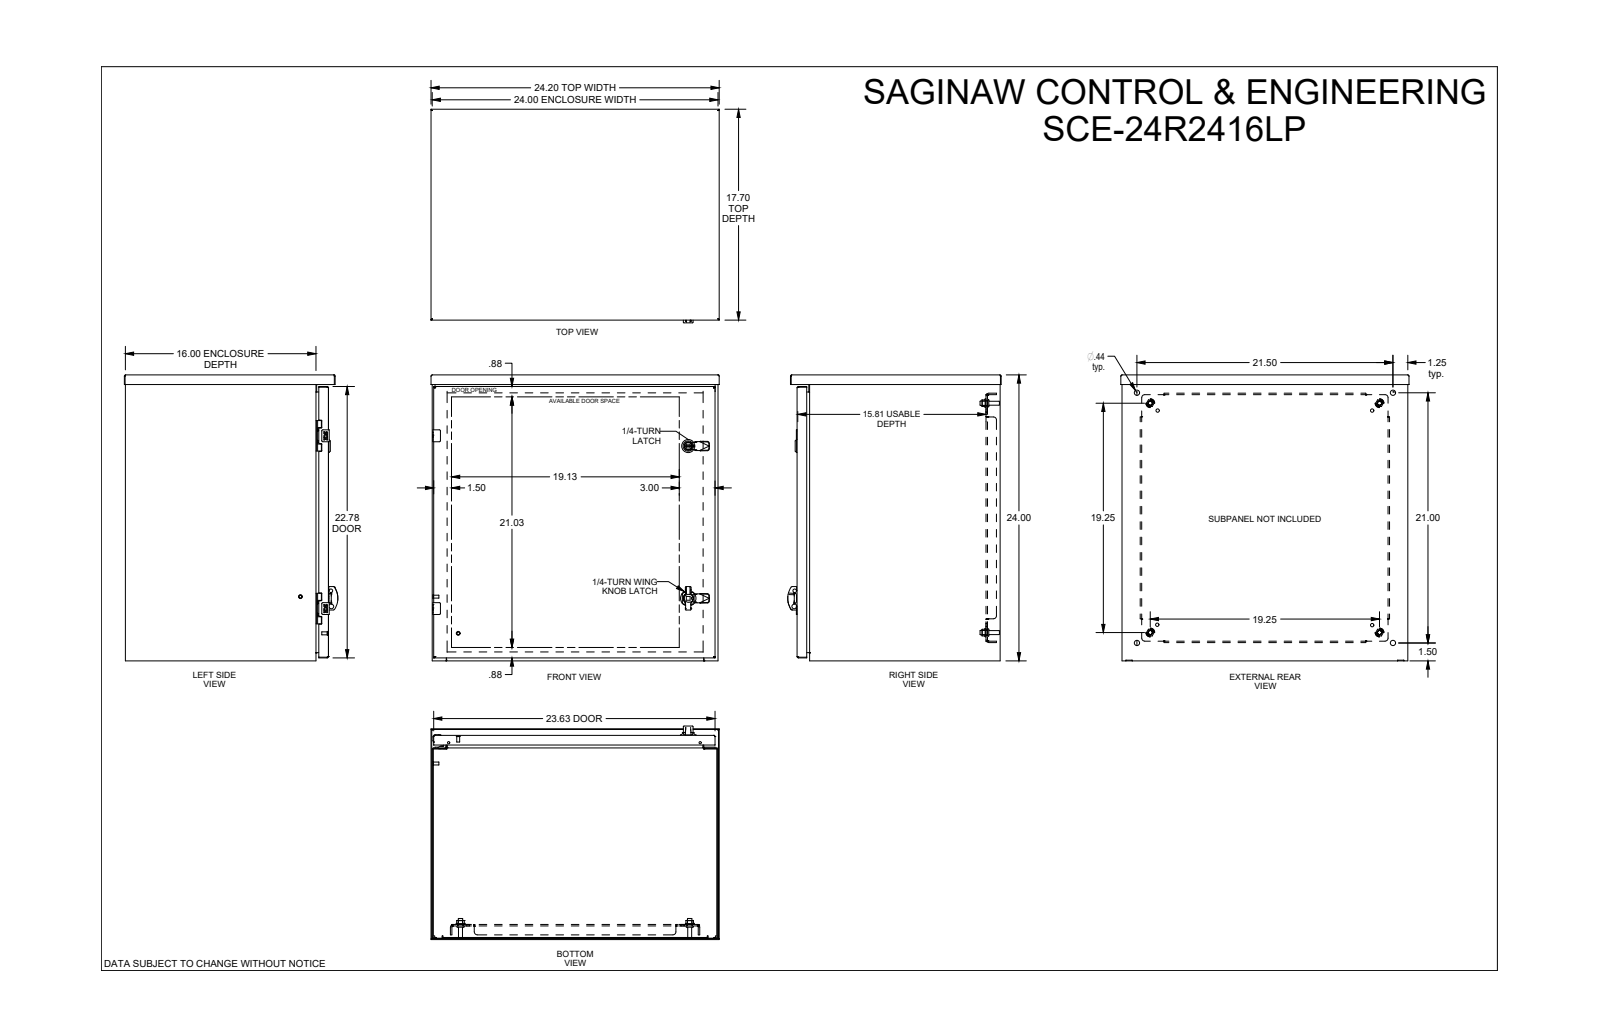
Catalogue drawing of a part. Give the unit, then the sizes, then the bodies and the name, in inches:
Units: inches
Overall size (bounding box): 24.2 × 24 × 17.927
Round holes (diameter × count): ⌀0.172 ×4, ⌀0.205 ×4, ⌀0.244 ×4, ⌀0.266 ×4, ⌀0.281 ×4, ⌀0.367 ×4, ⌀0.375 ×4, ⌀0.438 ×4, ⌀0.5 ×4, ⌀0.04 ×2, ⌀0.156 ×2, ⌀0.218 ×2
Round bosses / shafts (diameter × count): ⌀0.17 ×6, ⌀0.366 ×4, ⌀0.332 ×4, ⌀0.25 ×4, ⌀0.24 ×4, ⌀0.196 ×3, ⌀0.866 ×2, ⌀0.802 ×2
Partial cylindrical surfaces — rounded edges, fillets, slot ends (radius × count): R0.015 ×72, R0.012 ×60, R0.01 ×26, R0.02 ×24, R0.112 ×23, R0.06 ×22, R0.052 ×19, R0.03 ×15
Main face-to-face distances: 0.06, 23.94, 24, 23.88, 0.06, 16.933, 16.993, 17.053, 16.993, 0.125
Hole centre spacings: 14.5, 0.024, 0.493, 0.985, 18.641, 20.394, 28.638, 0.875
Bodies: 0 solids, 2429 faces (1160 planar, 823 cylindrical, 446 other)
Part name (STEP PRODUCT): SCE-24R2416LP
STEP written by: SolidWorks 2019 (CONFIG_CONTROL_DESIGN)
